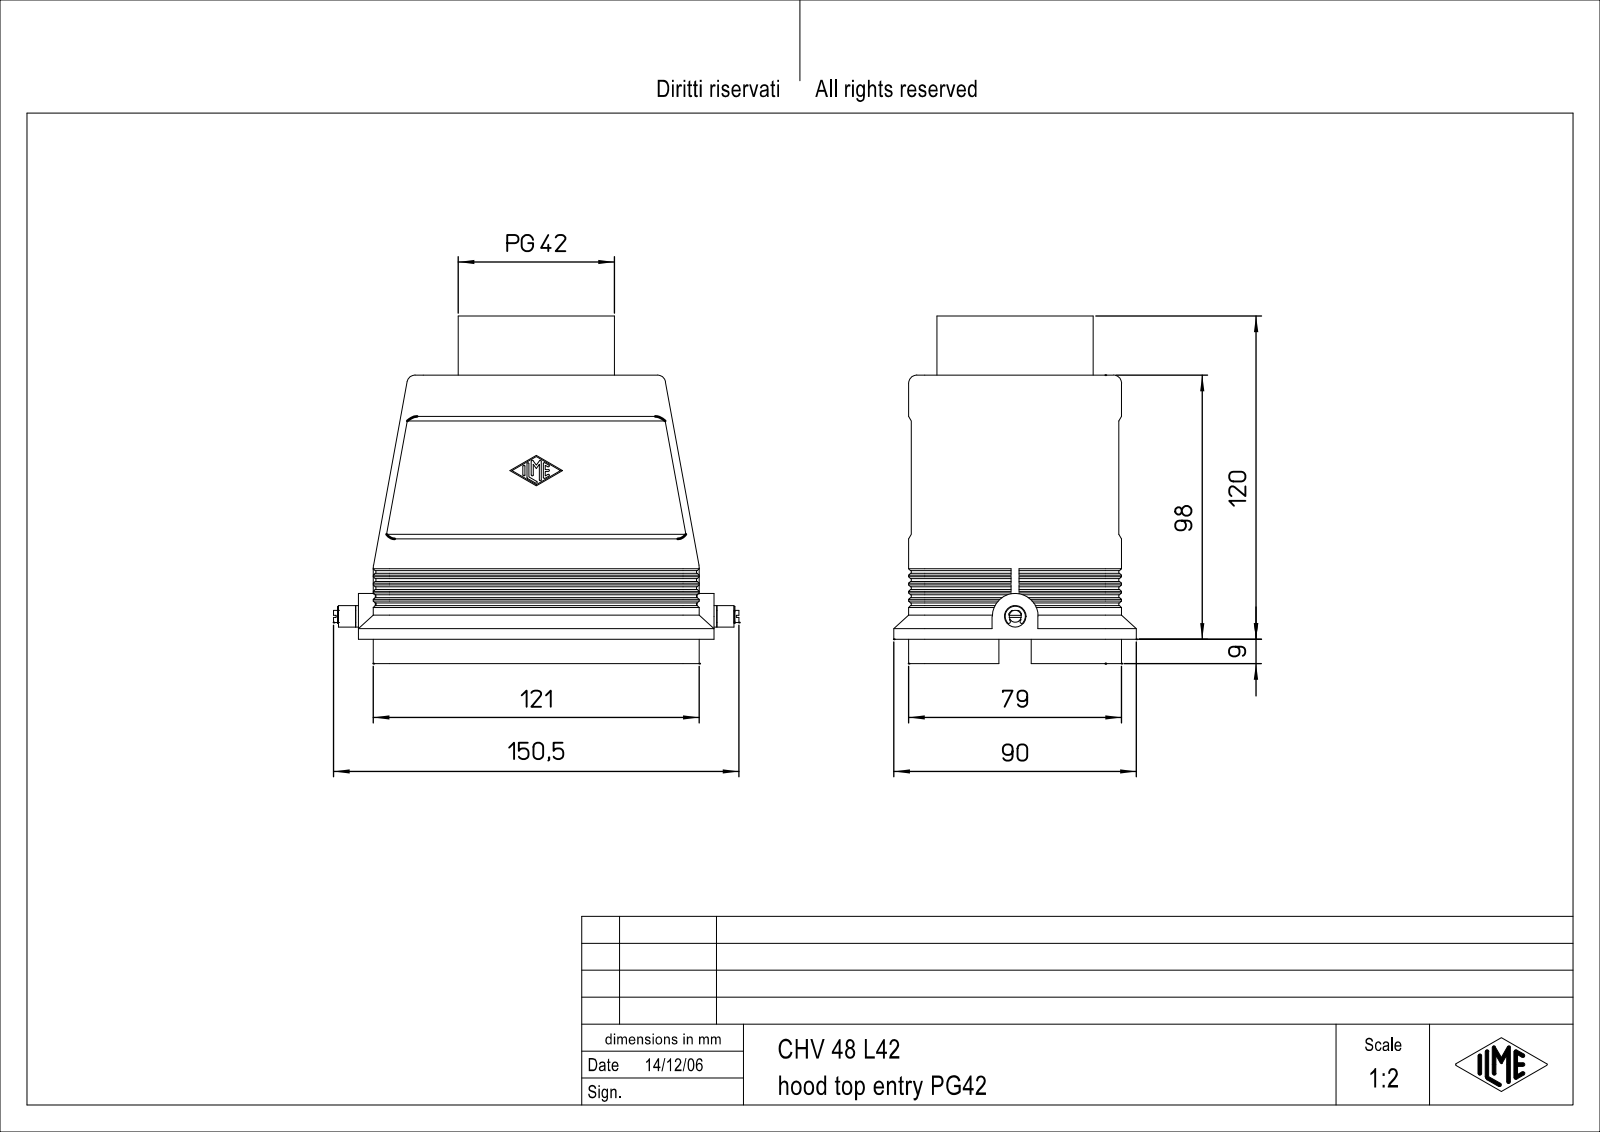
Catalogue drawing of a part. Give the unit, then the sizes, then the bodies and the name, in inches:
Units: inches
Overall size (bounding box): 5.925 × 5.079 × 3.543
Round holes (diameter × count): ⌀0.097 ×8, ⌀0.138 ×8, ⌀2.059 ×1, ⌀2.126 ×1
Round bosses / shafts (diameter × count): ⌀2.283 ×1, ⌀1.772 ×1, ⌀0.315 ×1, ⌀0.236 ×1, ⌀0.177 ×1, ⌀0.138 ×1
Partial cylindrical surfaces — rounded edges, fillets, slot ends (radius × count): R0.015 ×14, R0.079 ×12, R0.236 ×8, R0.02 ×4, R0.118 ×4, R0.197 ×4, R0.453 ×4, R0.037 ×3
Main face-to-face distances: 0.098, 0.138, 2.933, 2.835, 0.039, 2.972, 3.071, 3.031, 0.335, 0.394
Hole centre spacings: 1.063, 1.378, 2.053, 2.383, 4.094, 4.23, 4.32, 0.315
Volume: 13.26 in³ · Surface area: 167.6 in²
Bodies: 1 solid, 646 faces (338 planar, 240 cylindrical, 68 other)
Part name (STEP PRODUCT): CHV_48_L42
STEP written by: CoCreate Modeling 16.00A 16-Aug-2008 (C) Parametric Technology GmbH (AUTOMOTIVE_DESIGN)
